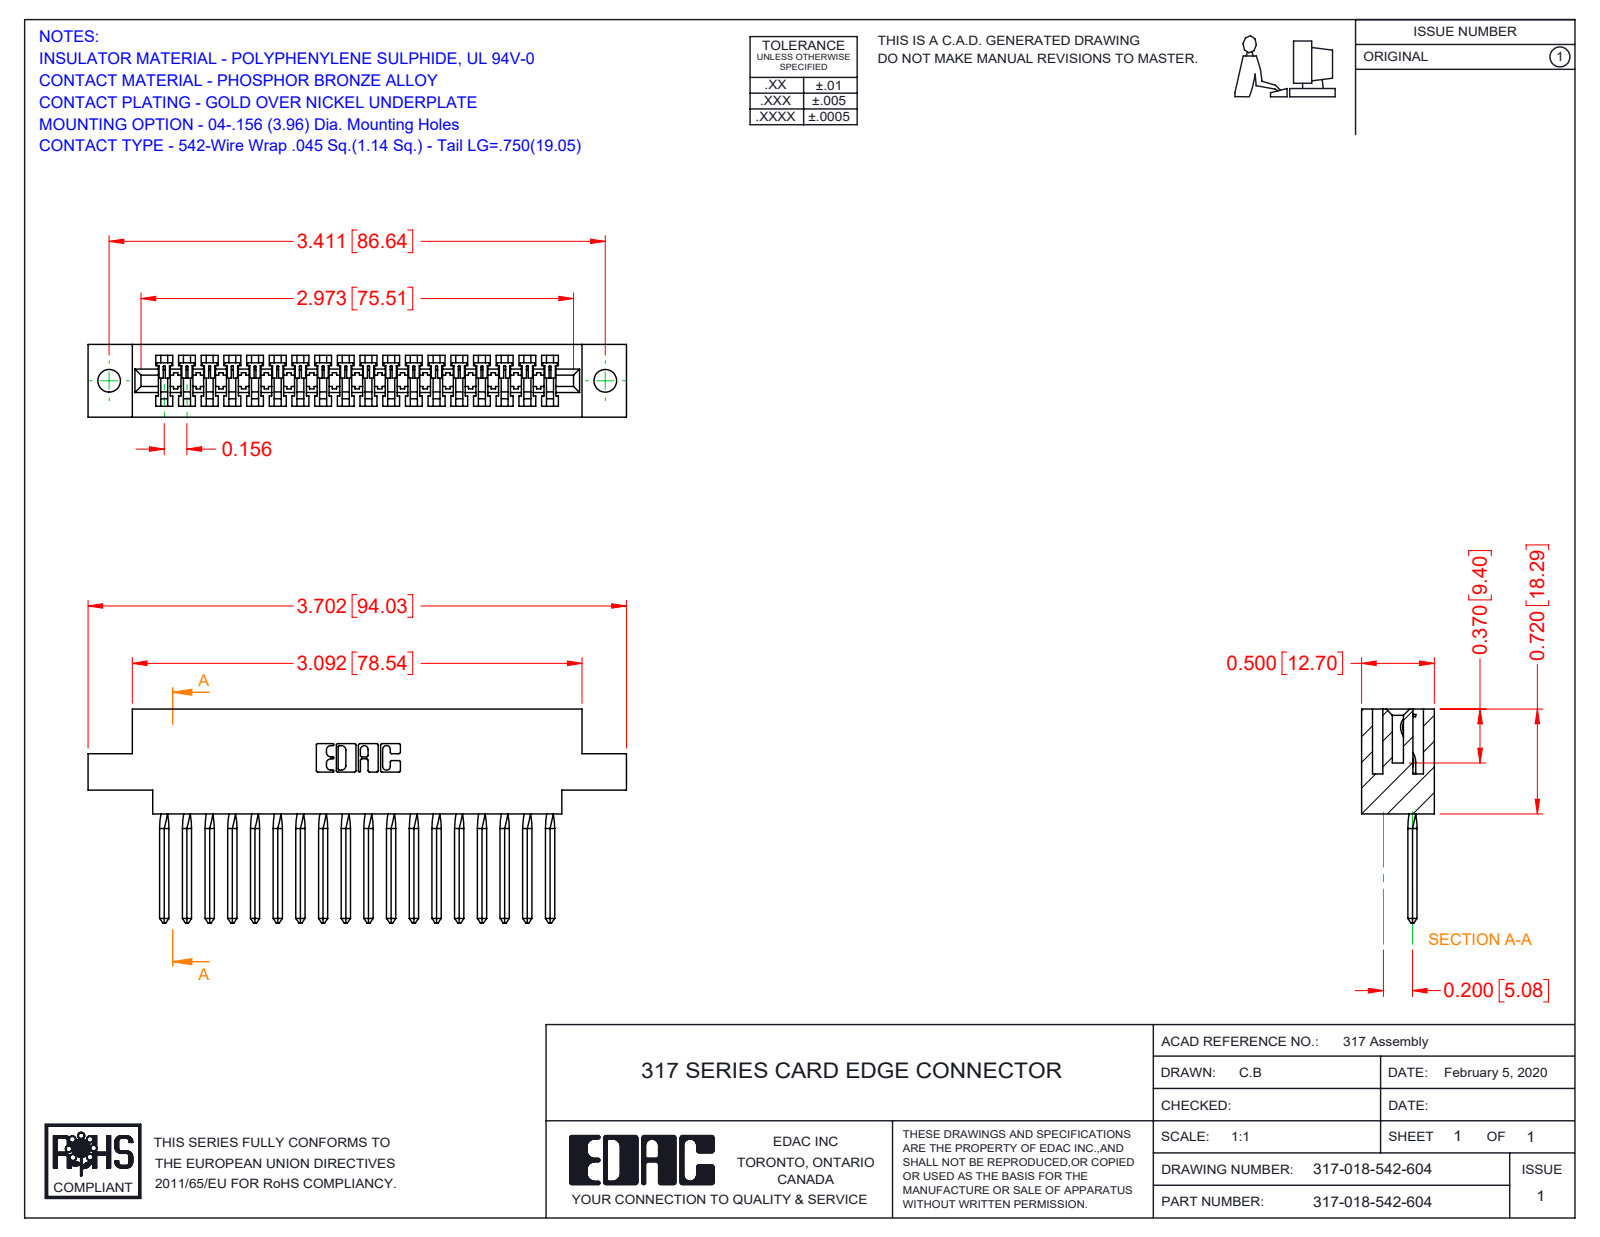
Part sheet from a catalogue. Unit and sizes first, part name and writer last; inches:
Units: inches
Overall size (bounding box): 3.702 × 1.47 × 0.5
Round holes (diameter × count): ⌀0.156 ×2
Partial cylindrical surfaces — rounded edges, fillets, slot ends (radius × count): R0.006 ×36, R0.01 ×22, R0.007 ×6, R0.031 ×6, R0.026 ×3, R0.074 ×1, R0.089 ×1, R0.1 ×1
Main face-to-face distances: 0.5, 0.075, 0.425, 0.11, 0.35, 0.136, 0.72, 0.065, 0.211, 0.289
Hole centre spacings: 3.411
Volume: 0.842 in³ · Surface area: 24.95 in²
Bodies: 19 solids, 1452 faces (1210 planar, 170 cylindrical, 72 other)
Part name (STEP PRODUCT): 317-018-542-604; 317-290-003_542; 317 Part_.156 Dia - TH
STEP written by: SolidWorks 2016 (CONFIG_CONTROL_DESIGN)
